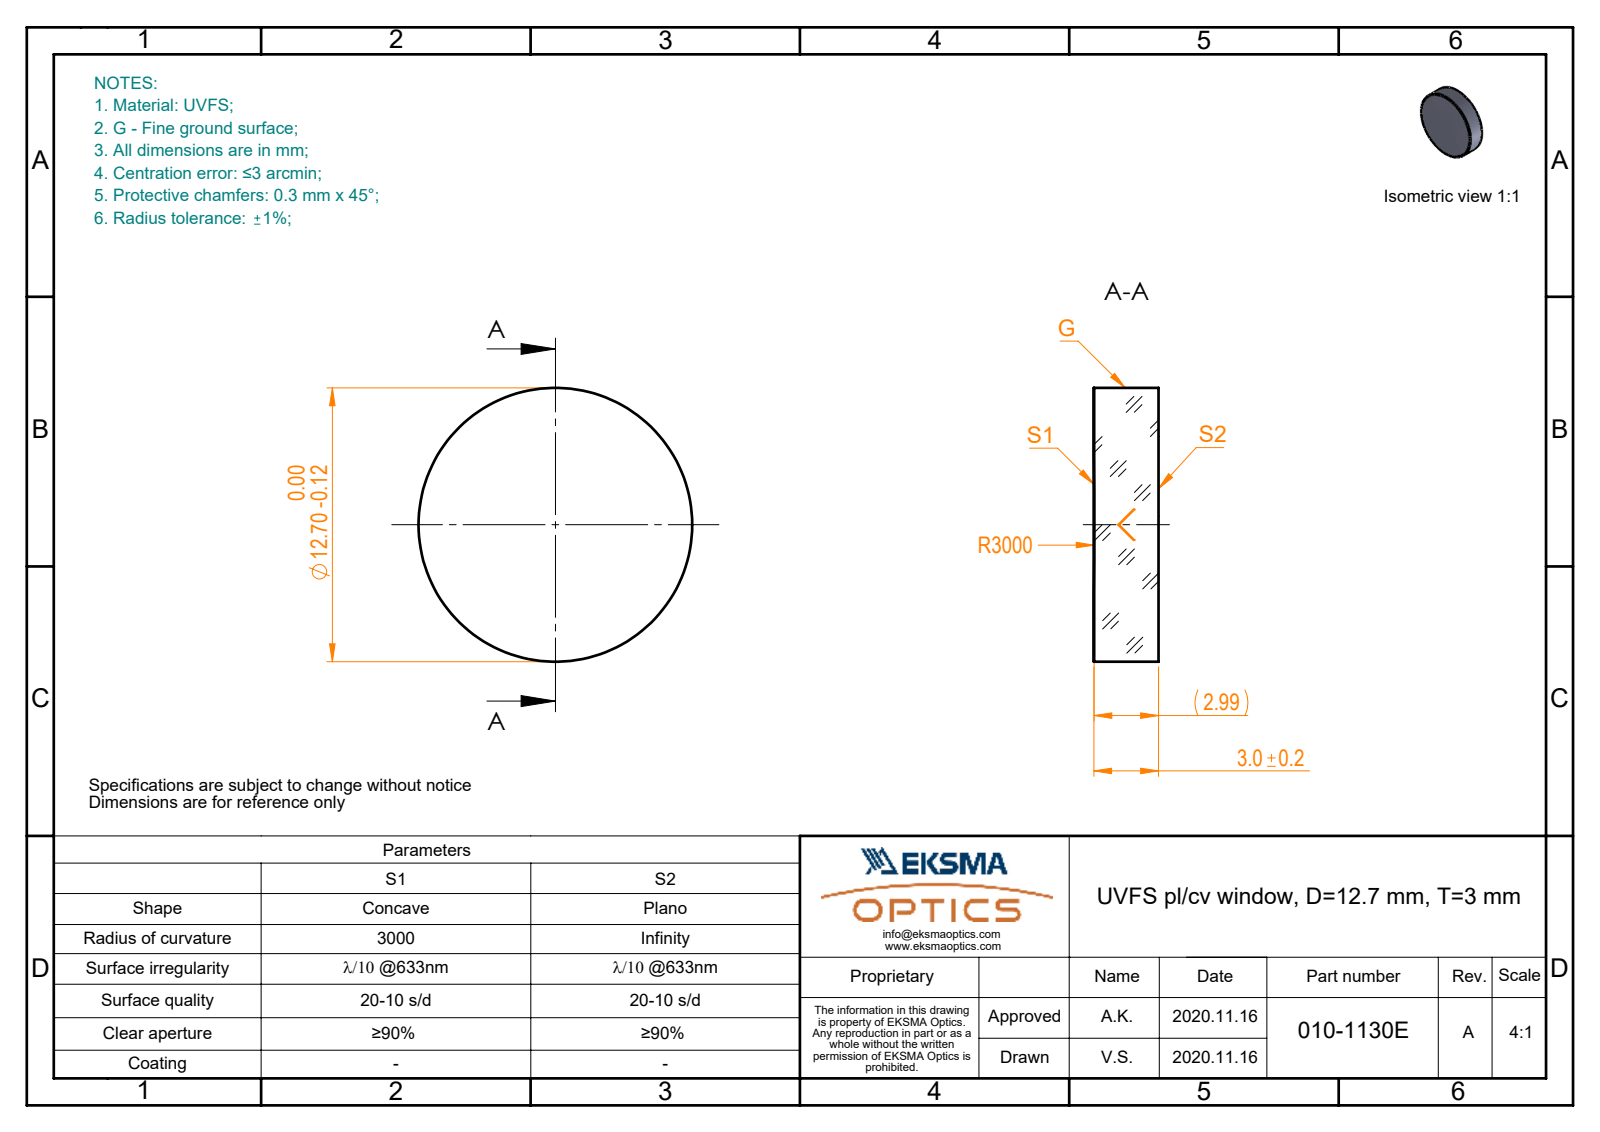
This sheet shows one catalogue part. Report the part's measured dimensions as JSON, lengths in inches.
{"part_name": "010-1130E_UVFS_PCV_window", "step_written_by": "SolidWorks 2019 (CONFIG_CONTROL_DESIGN)", "units": "inches", "bodies": {"solids": 1, "faces": 5, "planar": 1, "cylindrical": 2, "other": 2}, "overall_size": [0.5, 0.5, 0.118], "volume_in3": 0.023, "surface_area_in2": 0.578, "round_bosses_or_shafts": [[0.5, 1]]}
